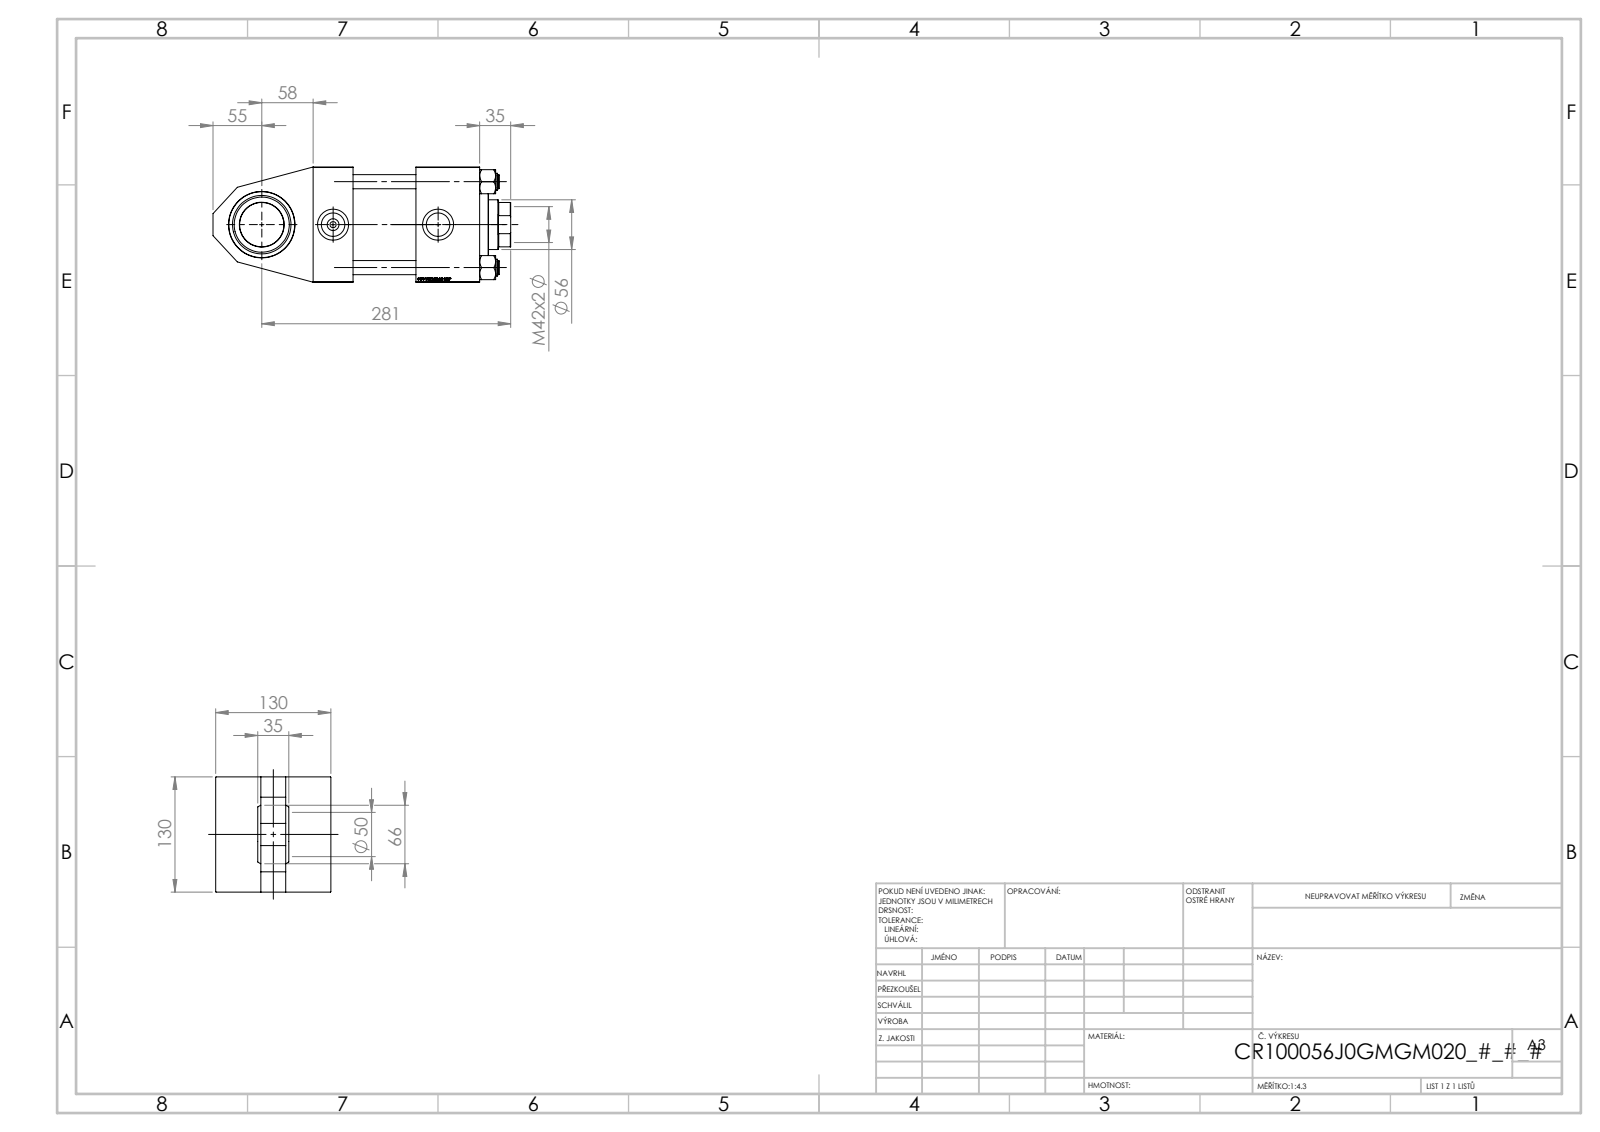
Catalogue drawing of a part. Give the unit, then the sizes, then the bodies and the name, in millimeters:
Units: millimetres
Overall size (bounding box): 336 × 130 × 130
Round holes (diameter × count): ⌀16 ×4, ⌀2.5 ×2, ⌀7 ×2, ⌀26.44 ×2, ⌀35 ×2, ⌀40.5 ×1, ⌀50 ×1, ⌀56 ×1, ⌀59 ×1, ⌀75 ×1, ⌀76 ×1, ⌀85.5 ×1
Round bosses / shafts (diameter × count): ⌀19 ×4, ⌀106 ×1, ⌀72 ×1
Partial cylindrical surfaces — rounded edges, fillets, slot ends (radius × count): R27 ×1
Main face-to-face distances: 130, 51, 79, 45, 188, 143, 116, 71, 72, 28
Hole centre spacings: 49.02, 68.52, 96.9, 101.73, 41, 137.04, 80.5, 82
Volume: 2 752 000 mm³ · Surface area: 379 183 mm²
Bodies: 12 solids, 1194 faces (565 planar, 89 cylindrical, 540 other)
Part name (STEP PRODUCT): V215_VC_A; V215CR_VCP_J; V215CR_J_Body; NUT_M5_J (+2 more)
STEP written by: SolidWorks 2019 (CONFIG_CONTROL_DESIGN)
